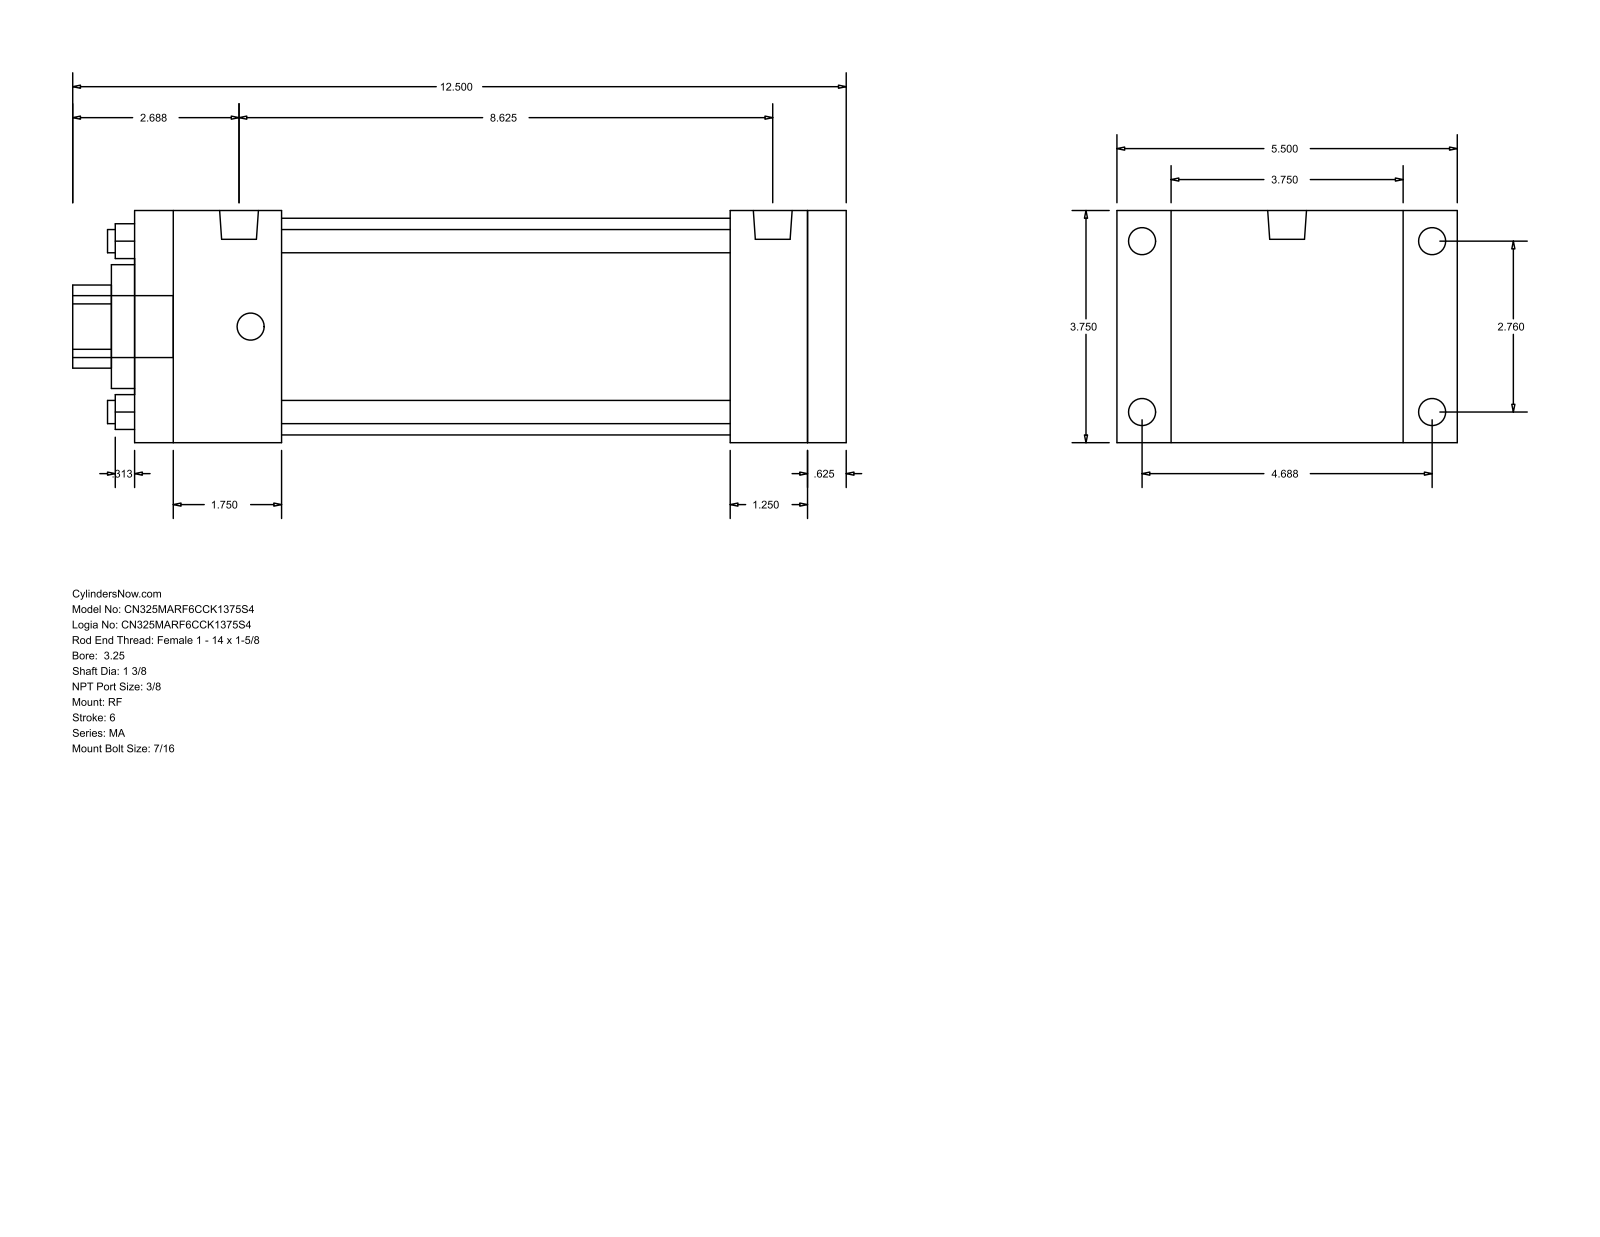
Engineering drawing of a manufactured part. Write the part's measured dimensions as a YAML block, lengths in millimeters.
part_name: "MA_RF__0325_1.375"
step_written_by: "GSSL Pune (CONFIG_CONTROL_DESIGN)"
units: millimeters
bodies: {solids: 0, faces: 92, planar: 64, cylindrical: 28, other: 0}
overall_size: [317.5, 139.7, 95.25]
round_holes:
  - {diameter: 9.53, count: 4}
  - {diameter: 34.92, count: 1}
  - {diameter: 50.8, count: 1}
  - {diameter: 88.9, count: 1}
round_bosses_or_shafts:
  - {diameter: 11.11, count: 8}
  - {diameter: 15.93, count: 2}
  - {diameter: 25.4, count: 1}
partial_cylinders:
  - {radius: 17.06, count: 1}
face_to_face_distances: [95.24, 292.1, 15.88, 276.22, 22.23, 117.47, 244.48, 31.74, 47.62, 60.32]
hole_center_spacings: [49.57, 70.1, 99.14]
